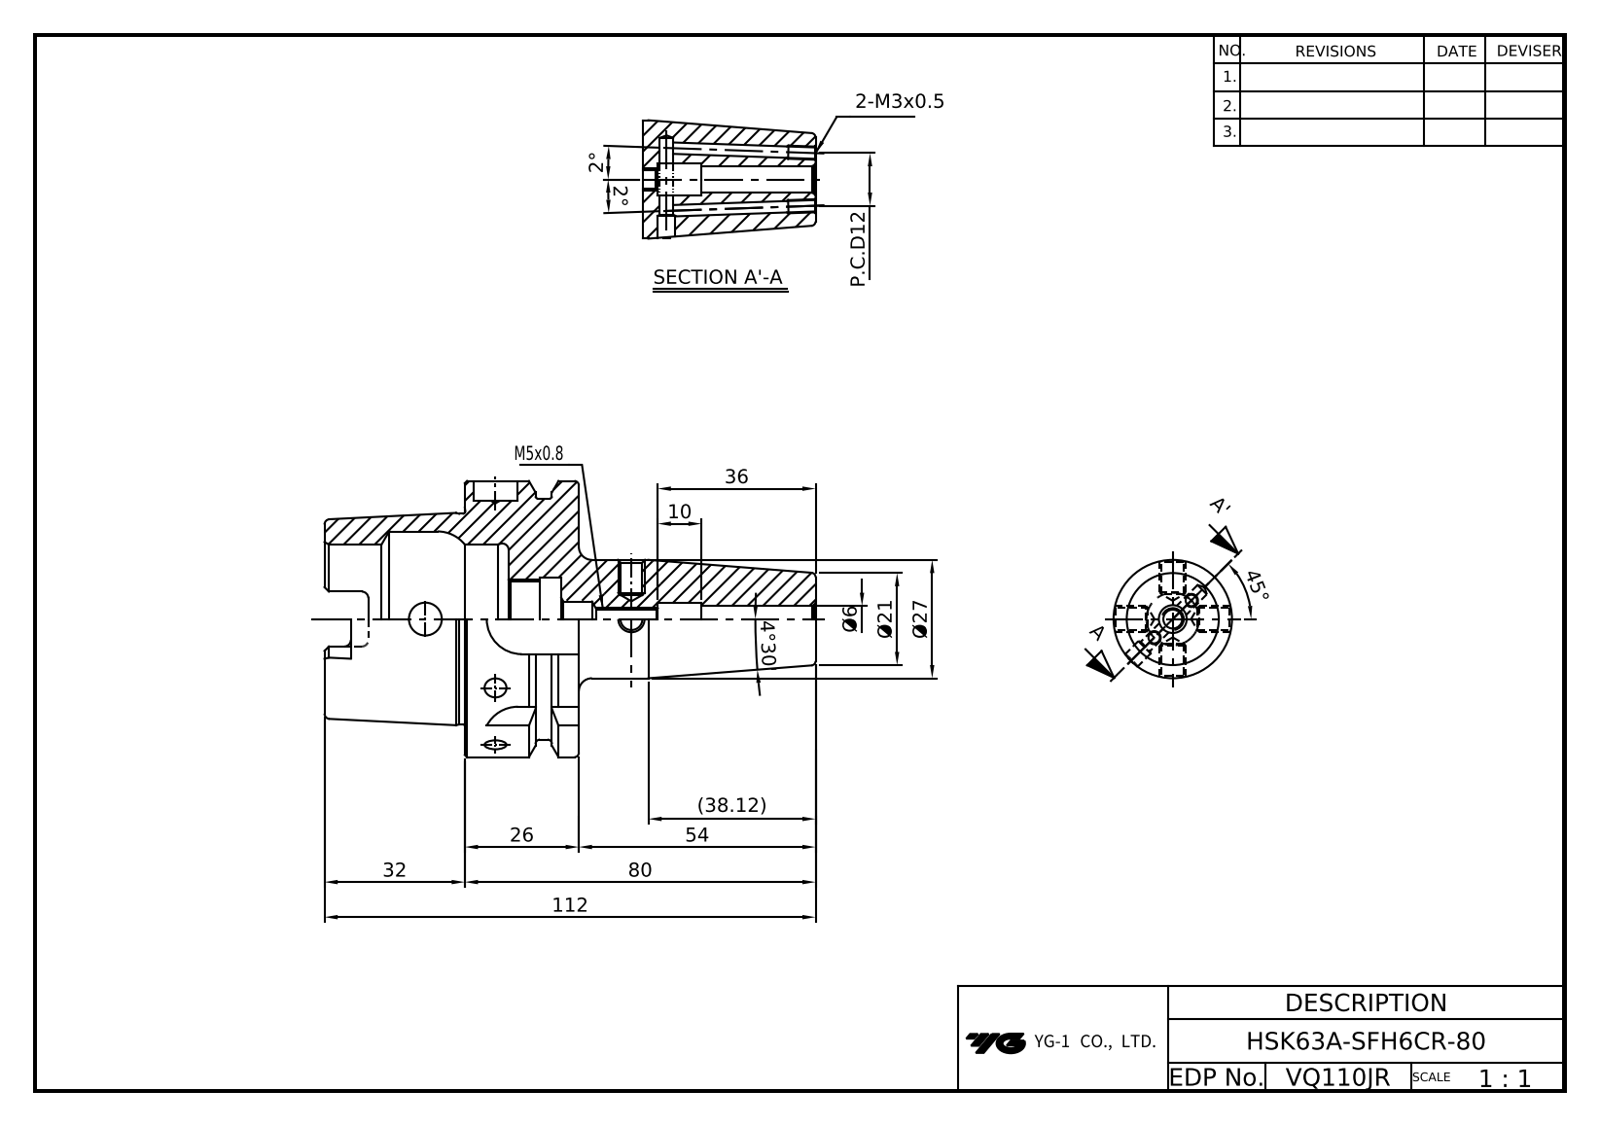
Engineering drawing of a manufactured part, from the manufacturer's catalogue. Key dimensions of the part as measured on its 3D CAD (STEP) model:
Part name (STEP PRODUCT): LO-HSK63A-SFH6CR-80
STEP written by: Autodesk Inventor 2022 (AUTOMOTIVE_DESIGN)
Units: millimetres
Bodies: 1 solid, 121 faces (42 planar, 36 cylindrical, 43 other)
Overall size (bounding box): 112 × 63 × 63
Volume: 106 210 mm³ · Surface area: 27 752 mm²
Round holes (diameter × count): ⌀2.46 ×2, ⌀4.13 ×1, ⌀6 ×1, ⌀7.2 ×1, ⌀7.5 ×1, ⌀8 ×1, ⌀10 ×1, ⌀16.92 ×1, ⌀19 ×1, ⌀34 ×1, ⌀40 ×1
Round bosses / shafts (diameter × count): ⌀63 ×1, ⌀55 ×1, ⌀48.04 ×1, ⌀27 ×1
Partial cylindrical surfaces — rounded edges, fillets, slot ends (radius × count): R1.5 ×6, R2.88 ×4, R8 ×4
Main face-to-face distances: 26, 10, 58, 16, 54, 32, 42, 22, 53, 4
